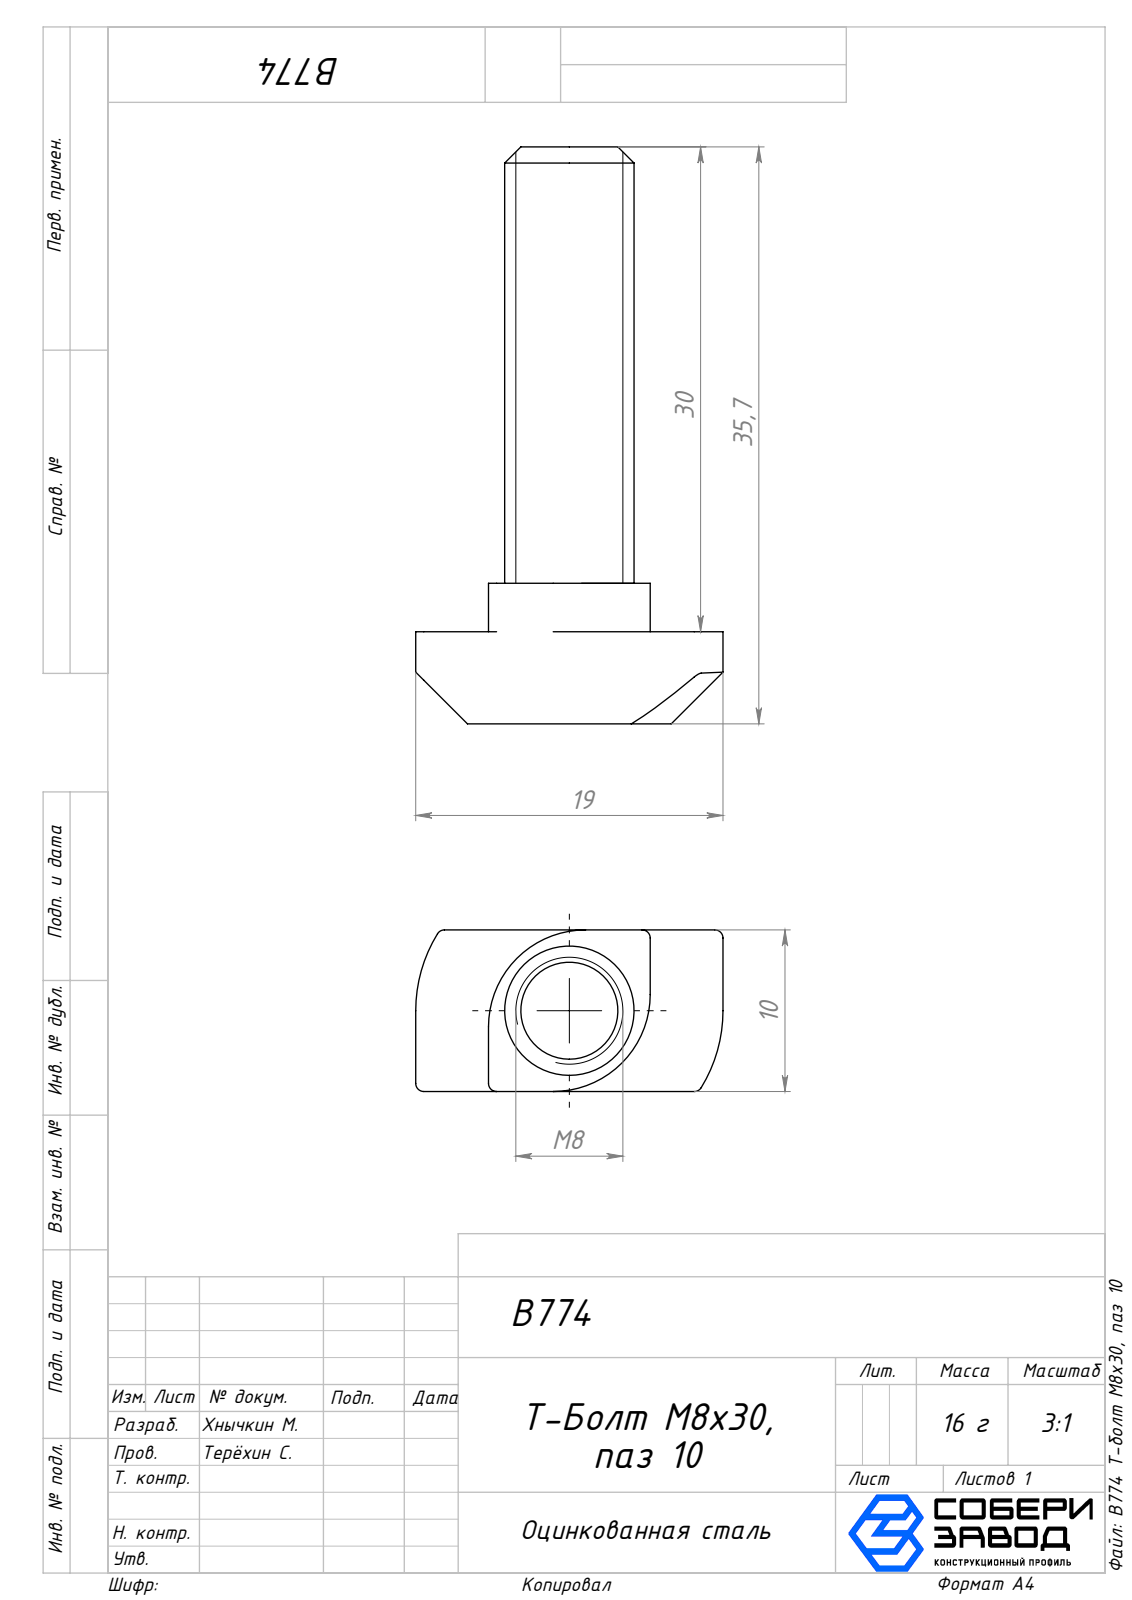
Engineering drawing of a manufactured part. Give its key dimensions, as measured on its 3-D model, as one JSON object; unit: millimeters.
{"part_name": "B774 Т-болт М8х30, паз 10", "step_written_by": "SolidWorks 2025 (AUTOMOTIVE_DESIGN)", "units": "millimeters", "bodies": {"solids": 1, "faces": 29, "planar": 13, "cylindrical": 12, "other": 4}, "overall_size": [35.7, 19, 10], "volume_mm3": 2549, "surface_area_mm2": 1391, "round_bosses_or_shafts": [[8, 1]], "partial_cylinders_radius": [[0.5, 6], [6, 2], [9.08, 2]], "face_to_face_distances": [10, 5.7, 8.7, 3, 35.7, 30, 27, 4.5, 14.5, 19]}
